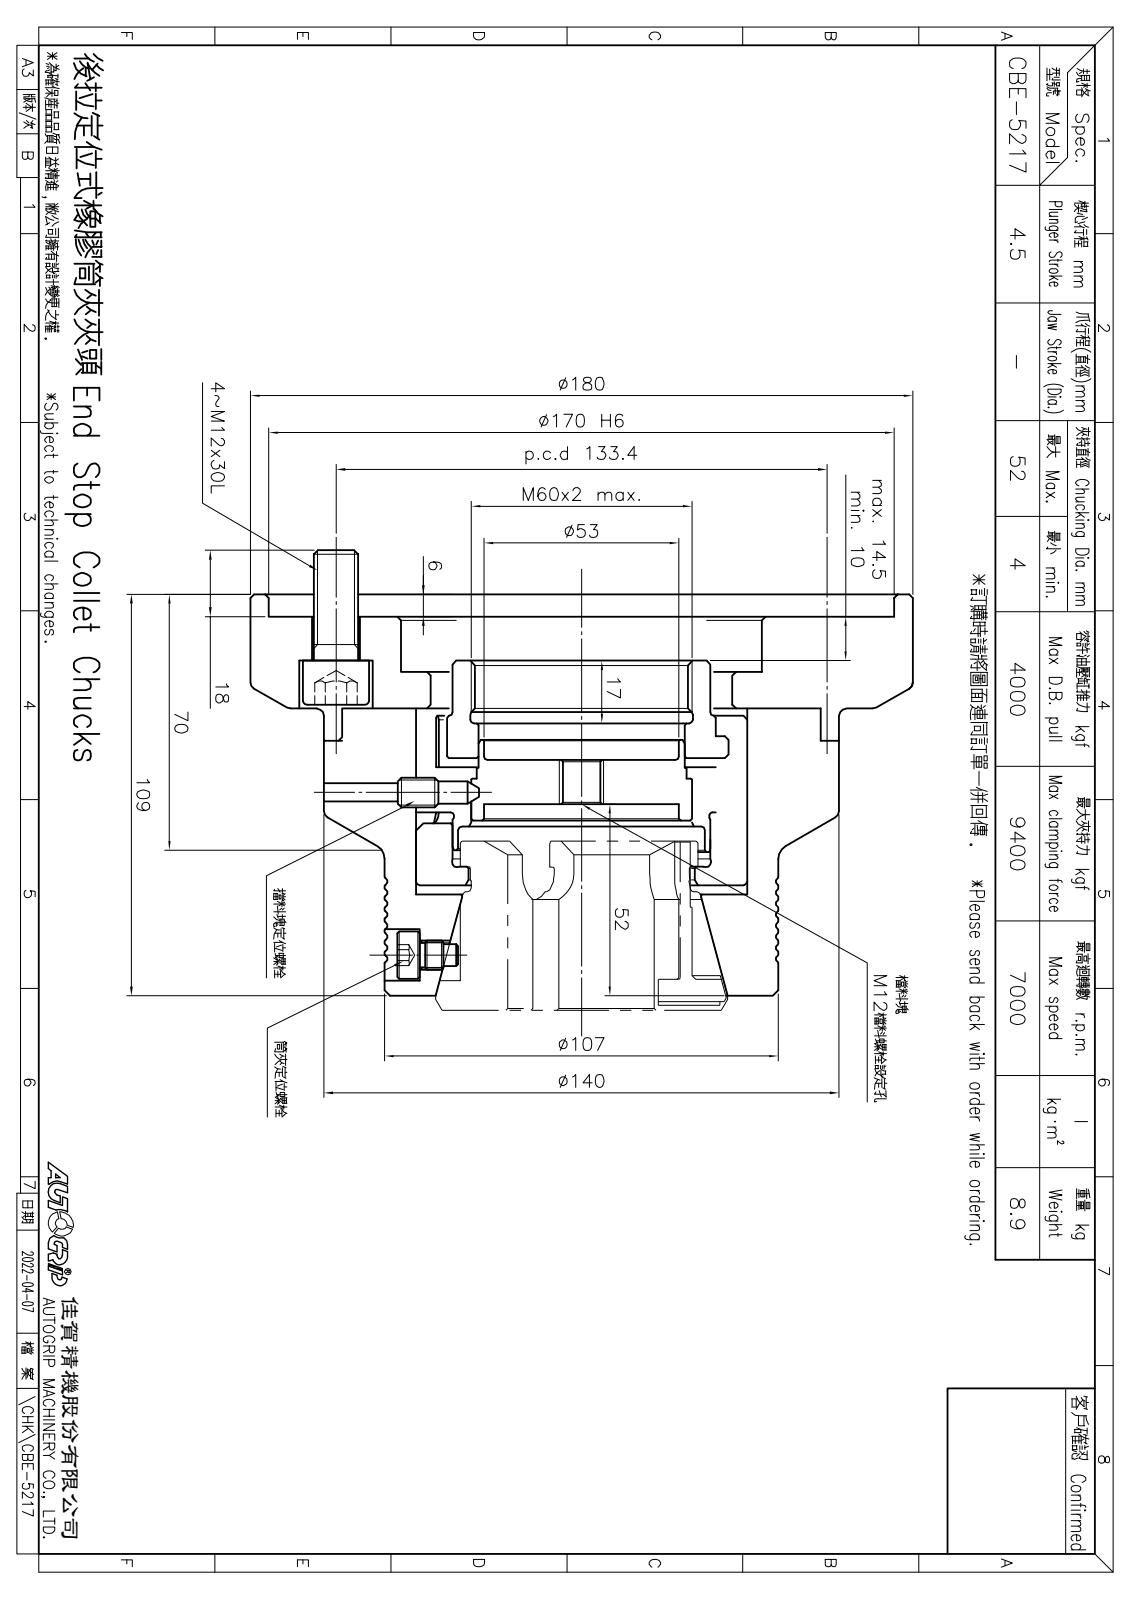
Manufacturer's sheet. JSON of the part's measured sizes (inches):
{"part_name": "CF-CBE-52-01000; CF-CBE-5217-01000; CF-CBE-5217-04010; CF-CBE-5217 (+1 more)", "step_written_by": "SolidWorks 2016 (CONFIG_CONTROL_DESIGN)", "units": "inches", "bodies": {"solids": 7, "faces": 357, "planar": 87, "cylindrical": 112, "other": 158}, "overall_size": [7.087, 7.087, 4.764], "volume_in3": 70.48, "surface_area_in2": 299.6, "round_holes": [[0.268, 4], [0.512, 4], [0.787, 4], [0.425, 1], [1.693, 1], [1.929, 1], [1.949, 1], [2.087, 1], [2.165, 1], [2.205, 1], [2.303, 1], [2.382, 1]], "round_bosses_or_shafts": [[0.709, 4], [0.472, 4], [7.087, 1], [5.512, 1], [4.213, 1], [2.539, 1]], "partial_cylinders_radius": [[0.197, 4]], "face_to_face_distances": [0.984, 1.693, 0.472, 1.339, 2.677, 0.591, 0.866, 1.22, 1.457, 4.055], "hole_center_spacings": [1.935, 4.645, 2.402, 2.626, 3.396, 3.713, 4.803, 5.252]}
